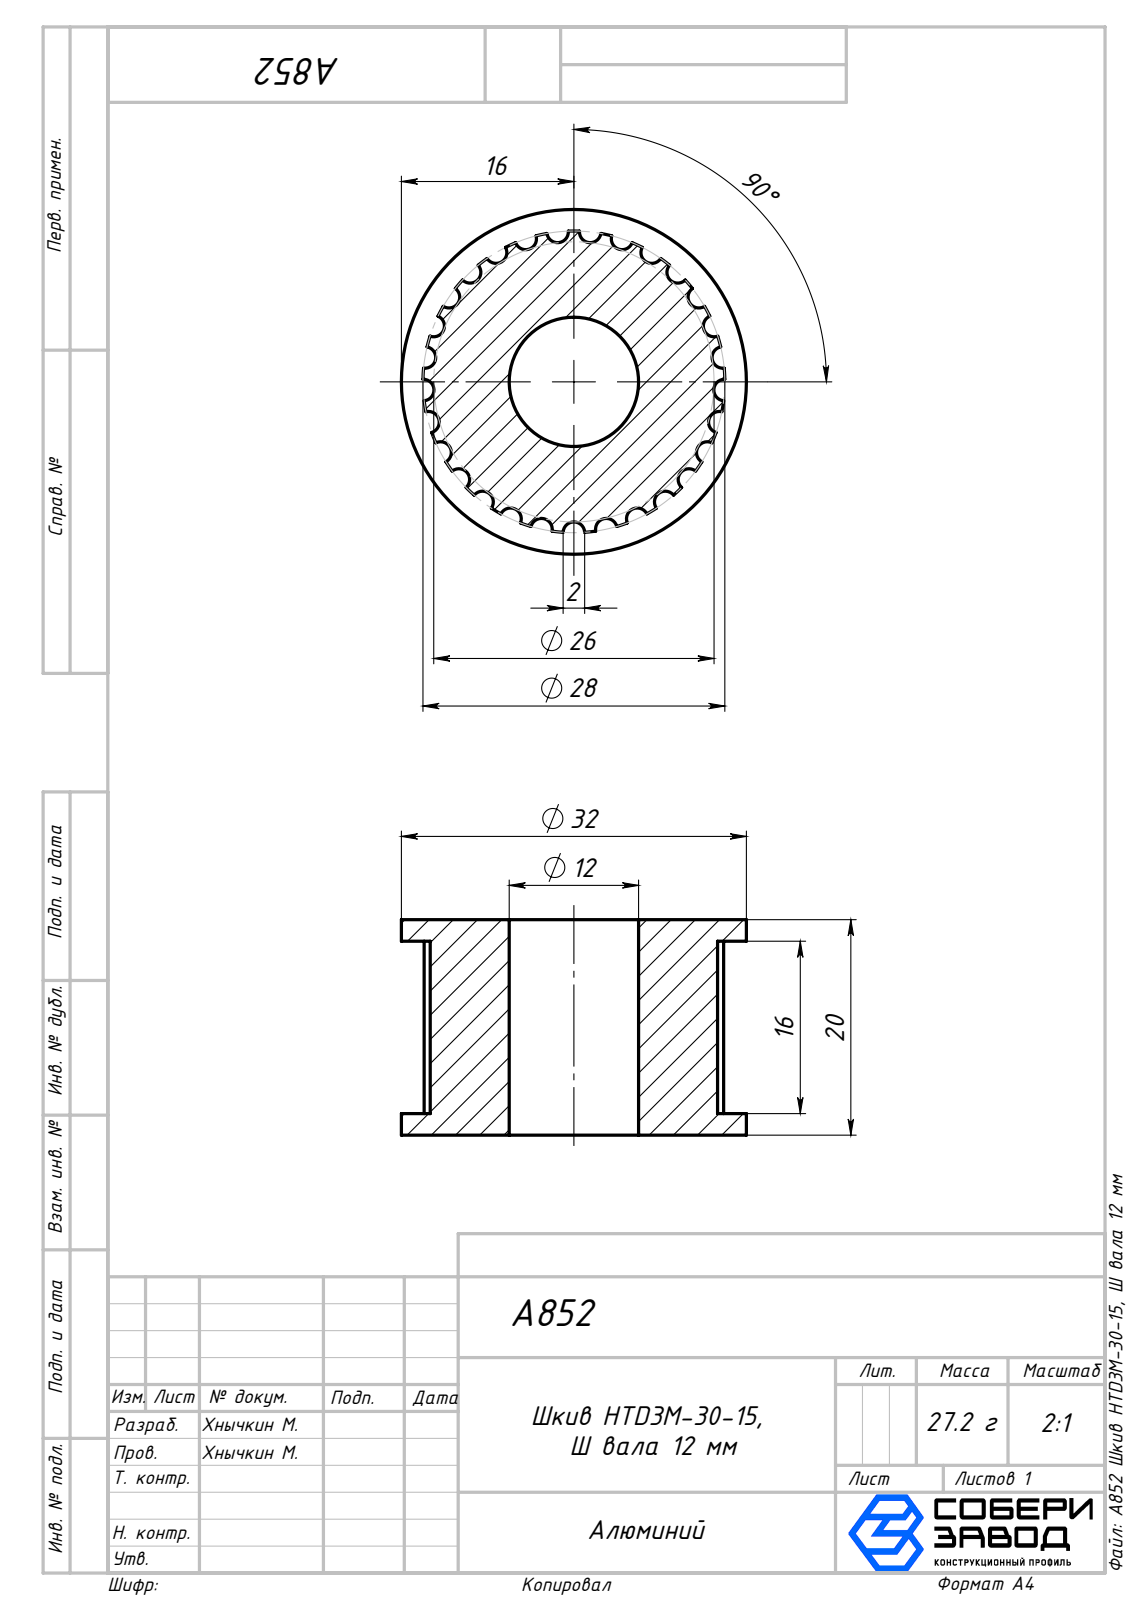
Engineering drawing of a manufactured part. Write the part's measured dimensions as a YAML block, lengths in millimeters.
part_name: "A852 Шкив HTD3M-30-15, Ø вала 12 мм"
step_written_by: "SolidWorks 2025 (AUTOMOTIVE_DESIGN)"
units: millimeters
bodies: {solids: 1, faces: 82, planar: 4, cylindrical: 78, other: 0}
overall_size: [32, 32, 20]
volume: 10089
surface_area: 4909
round_holes:
  - {diameter: 12, count: 1}
round_bosses_or_shafts:
  - {diameter: 32, count: 1}
partial_cylinders:
  - {radius: 1, count: 29}
  - {radius: 14, count: 1}
face_to_face_distances: [20, 2, 18, 16]
